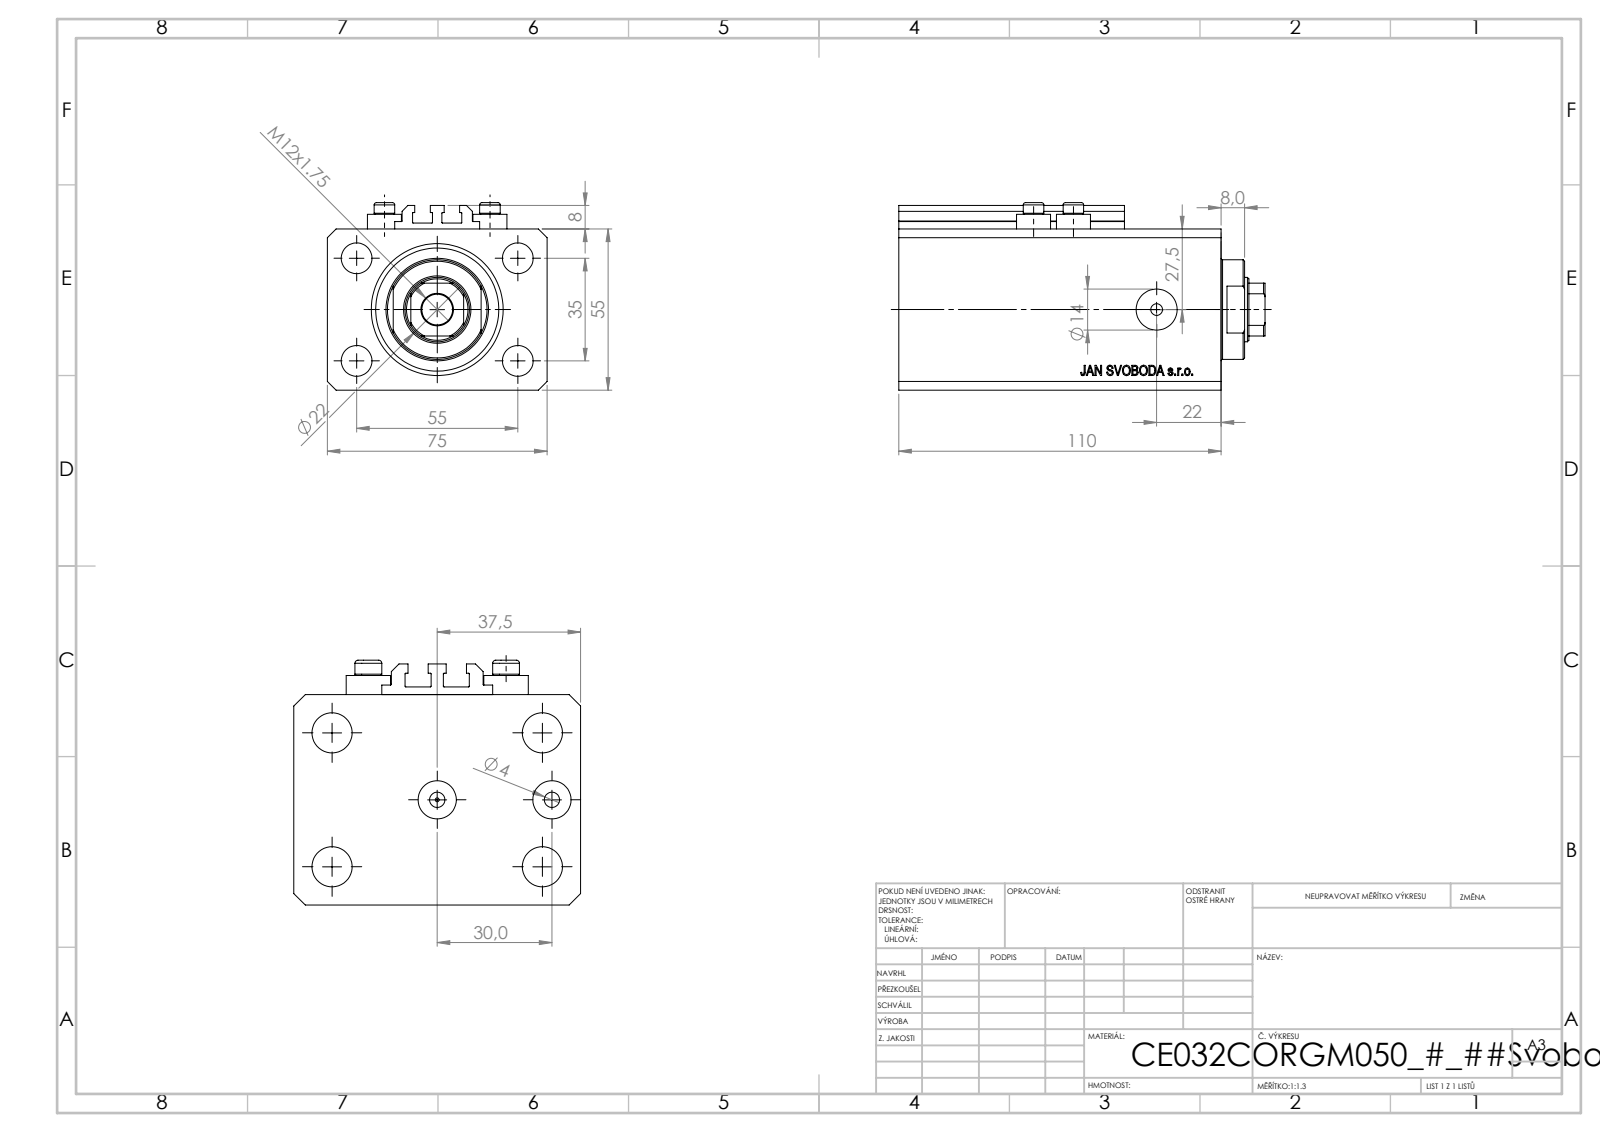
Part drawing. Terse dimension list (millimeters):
name: V250CE_C_Body; V250CE_VC_C; V250CE_C_VCP; ALLEN BOLT V250CE
written by: SolidWorks 2019 (CONFIG_CONTROL_DESIGN)
unit: mm
bodies: 8 solids, 1038 faces (504 planar, 88 cylindrical, 446 other)
size: 125 × 75 × 64
volume: 408 447 mm³; area: 91 607 mm²
holes: 8× ⌀4, 5× ⌀10.5, 2× ⌀10, 2× ⌀14, 1× ⌀1.25, 1× ⌀22, 1× ⌀32, 1× ⌀45
bosses: 4× ⌀11.6, 4× ⌀7, 1× ⌀34
rounds: 10× R0.2, 1× R10.5
face distances: 55, 75, 110, 15, 95, 9.9, 85.1, 100.1, 8, 3
hole spacings: 32.6, 13.6, 17.68, 35, 36, 38.48, 55, 60.1
